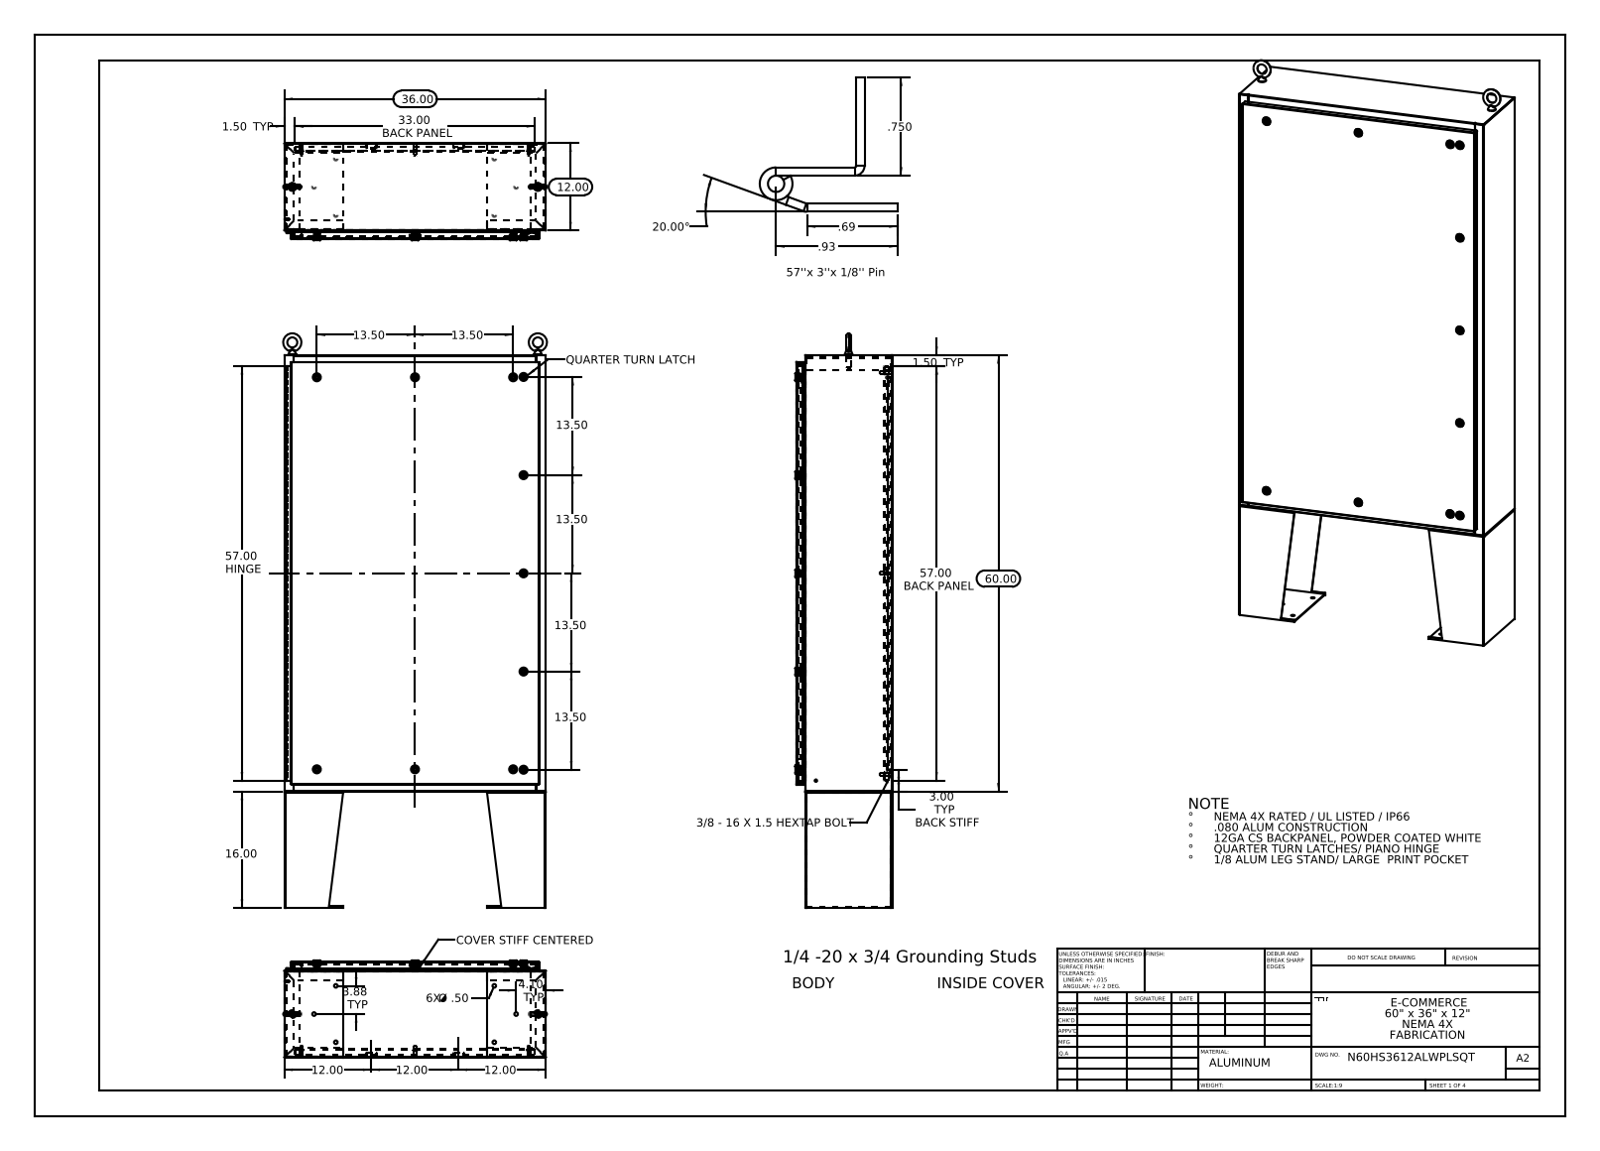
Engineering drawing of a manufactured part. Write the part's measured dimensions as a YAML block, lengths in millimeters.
part_name: "N60HS3612SSWPLSQT SD-LSK-ASSY; Eye-Bolt_Stiffener WMT Template 1923; N60HS3612SSWPLSQT Door Stiffener; N60HS3612SSWPLSQT Body (+8 more)"
step_written_by: "SolidWorks 2013 (CONFIG_CONTROL_DESIGN)"
units: millimeters
bodies: {solids: 36, faces: 2369, planar: 1193, cylindrical: 980, other: 196}
overall_size: [2006.6, 921.3, 335.3]
volume: 14990000
surface_area: 14210000
round_holes:
  - {diameter: 12.7, count: 14}
  - {diameter: 6.4, count: 8}
  - {diameter: 19.1, count: 4}
  - {diameter: 3.2, count: 1}
  - {diameter: 3.2, count: 1}
round_bosses_or_shafts:
  - {diameter: 15.9, count: 10}
  - {diameter: 9.5, count: 8}
  - {diameter: 8.4, count: 8}
  - {diameter: 4, count: 8}
  - {diameter: 3.6, count: 8}
  - {diameter: 8, count: 2}
  - {diameter: 6, count: 2}
  - {diameter: 6.4, count: 1}
partial_cylinders:
  - {radius: 0.3, count: 36}
  - {radius: 2.2, count: 30}
  - {radius: 11.2, count: 11}
  - {radius: 1, count: 8}
  - {radius: 3.6, count: 8}
  - {radius: 0.5, count: 6}
  - {radius: 3, count: 4}
  - {radius: 3.2, count: 4}
face_to_face_distances: [1.9, 333.4, 2.6, 331.5, 27.3, 335.3, 308, 25.4, 306.1, 29.9]
hole_center_spacings: [56.5, 181.3, 637.4, 701.7, 1059.4, 1458.4, 440.2, 443.8]
